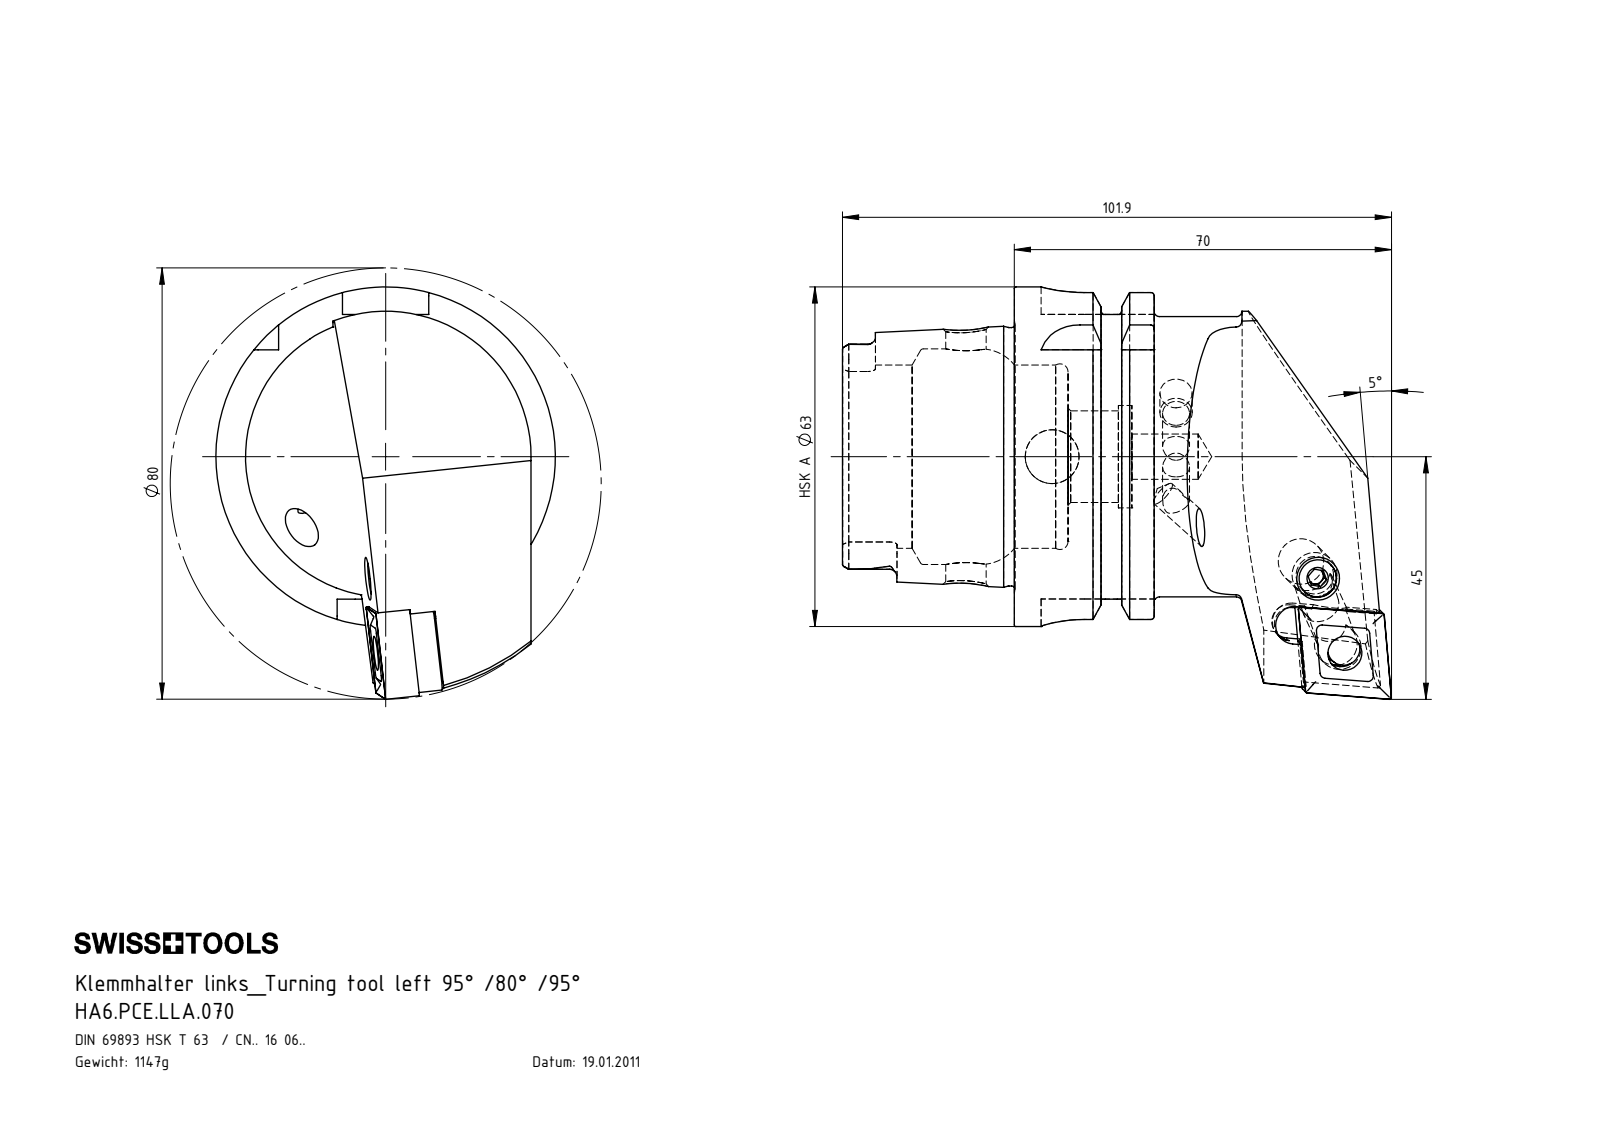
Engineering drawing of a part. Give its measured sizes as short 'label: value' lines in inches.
name: HA6-PCE.LLA.070; KVT_MB_600_060; WCE-ER2.101.004_A; CNMG160604 (+3 more)
written by: SolidWorks 2012 (CONFIG_CONTROL_DESIGN)
unit: in
bodies: 7 solids, 362 faces (114 planar, 101 cylindrical, 147 other)
size: 4.012 × 3.012 × 2.48
volume: 8.847 in³; area: 52.9 in²
holes: 2× ⌀0.197, 2× ⌀0.331, 1× ⌀0.25, 1× ⌀0.276, 1× ⌀0.295, 1× ⌀0.317, 1× ⌀0.394, 1× ⌀0.669, 1× ⌀0.748, 1× ⌀1.339, 1× ⌀1.575
bosses: 2× ⌀0.236, 1× ⌀2.48, 1× ⌀2.163, 1× ⌀2.047, 1× ⌀1.887, 1× ⌀0.315, 1× ⌀0.311, 1× ⌀0.252
rounds: 6× R0.055, 4× R0.016, 4× R0.059, 4× R0.113, 4× R0.315, 3× R0.138, 1× R0.122, 1× R0.148
face distances: 1.022, 0.63, 0.392, 1.256, 1.648, 2.278, 0.858, 2.079, 0.594, 0.187
hole spacings: 0.581, 0.59
